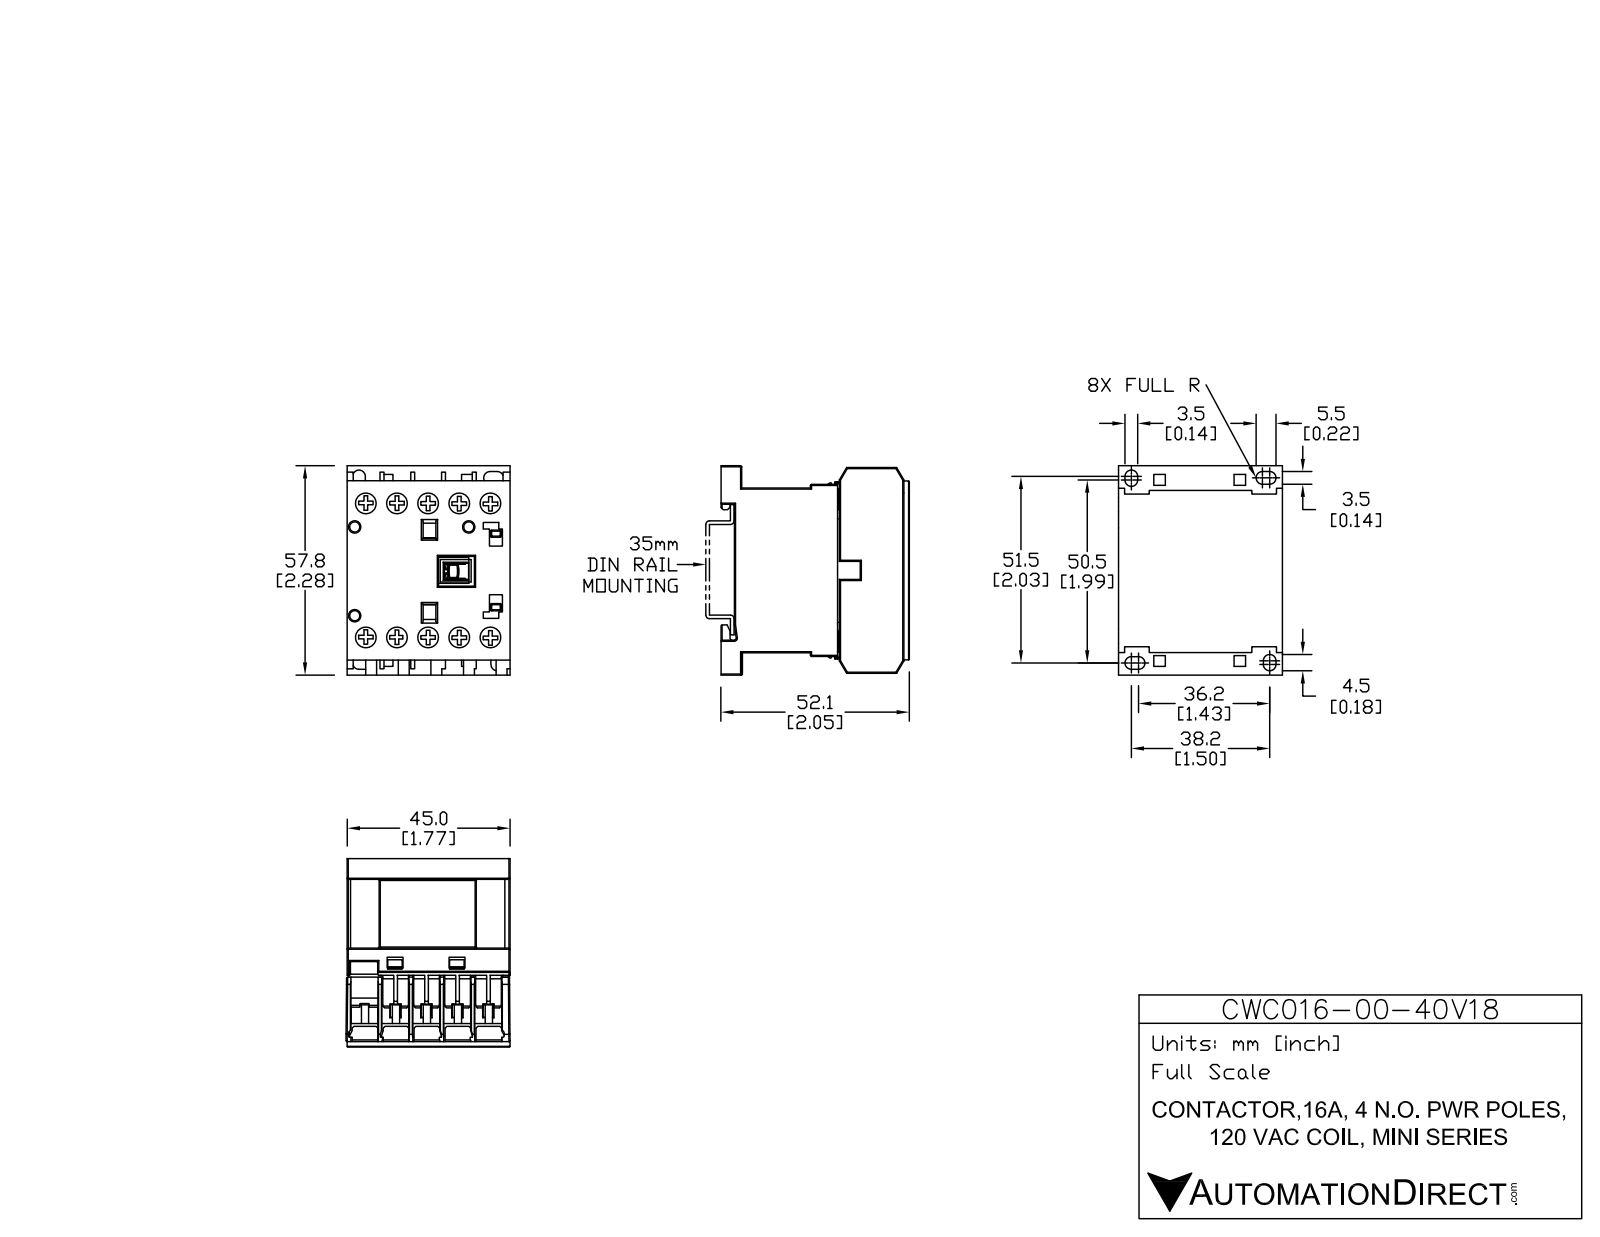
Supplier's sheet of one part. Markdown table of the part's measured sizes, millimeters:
| quantity | value |
| --- | --- |
| part name | CWC16-00-40V18 |
| STEP written by | SolidWorks 2013 (AUTOMOTIVE_DESIGN) |
| units | millimeters |
| bodies | 15 solids, 535 faces (445 planar, 90 cylindrical, 0 other) |
| overall size | 58.04 × 52.12 × 45.75 |
| volume | 97 133 mm³ |
| surface area | 30 437 mm² |
| round holes (diameter × count) | 6.2 × 10, 2.8 × 3 |
| round bosses / shafts (diameter × count) | 5.9 × 10 |
| partial cylindrical surfaces (radius × count) | 0.3 × 20, 1.72 × 6, 1.73 × 2, 0.32 × 1, 0.42 × 1, 0.55 × 1 |
| main face-to-face distances | 8.25, 45.5, 1.25, 16.5, 9.5, 5.5, 17.75, 5.13, 10.63, 7 |
| hole center spacings | 8.55, 37.94, 17.1, 40.72, 36.96, 25.65, 44.99, 6.91 |
